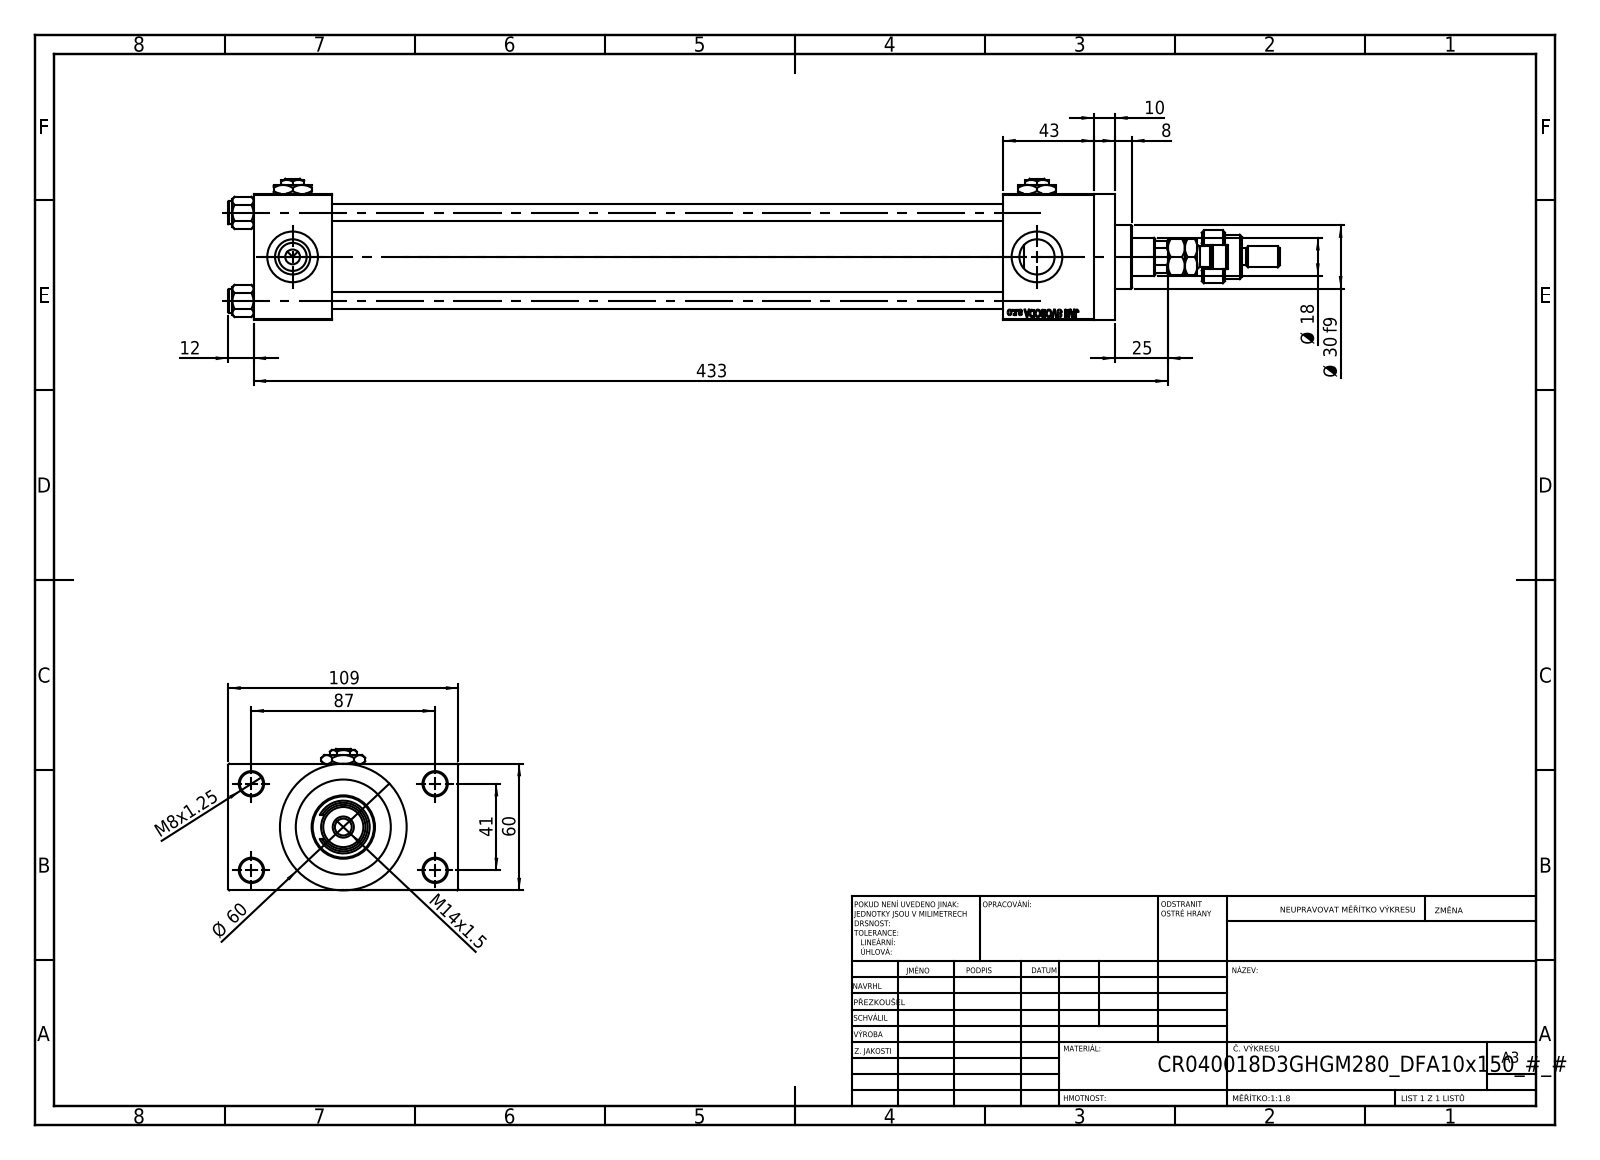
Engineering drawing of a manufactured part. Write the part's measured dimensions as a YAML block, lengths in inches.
part_name: "V215CR_VCP_D; FEMALE_PART_FOR_DFA; V215CR_D_Body; MFA (+4 more)"
step_written_by: "SolidWorks 2019 (CONFIG_CONTROL_DESIGN)"
units: inches
bodies: {solids: 15, faces: 1290, planar: 574, cylindrical: 112, other: 604}
overall_size: [19.606, 4.291, 2.638]
volume: 45.52
surface_area: 374.7
round_holes:
  - {diameter: 0.315, count: 4}
  - {diameter: 0.433, count: 4}
  - {diameter: 0.656, count: 4}
  - {diameter: 0.945, count: 4}
  - {diameter: 0.276, count: 3}
  - {diameter: 0.335, count: 1}
  - {diameter: 0.709, count: 1}
  - {diameter: 0.827, count: 1}
  - {diameter: 1.22, count: 1}
  - {diameter: 1.575, count: 1}
  - {diameter: 1.772, count: 1}
round_bosses_or_shafts:
  - {diameter: 0.433, count: 4}
  - {diameter: 2.362, count: 1}
  - {diameter: 1.811, count: 1}
  - {diameter: 1.181, count: 1}
  - {diameter: 0.984, count: 1}
  - {diameter: 0.63, count: 1}
  - {diameter: 0.394, count: 1}
  - {diameter: 0.315, count: 1}
partial_cylinders:
  - {radius: 0.217, count: 1}
  - {radius: 0.335, count: 1}
  - {radius: 0.344, count: 1}
face_to_face_distances: [2.362, 0.965, 12.52, 3.327, 1.457, 13.976, 1.693, 15.669, 14.213, 2.087]
hole_center_spacings: [0.892, 1.161, 1.642, 1.856, 1.893, 2.533, 3.011, 1.614]
